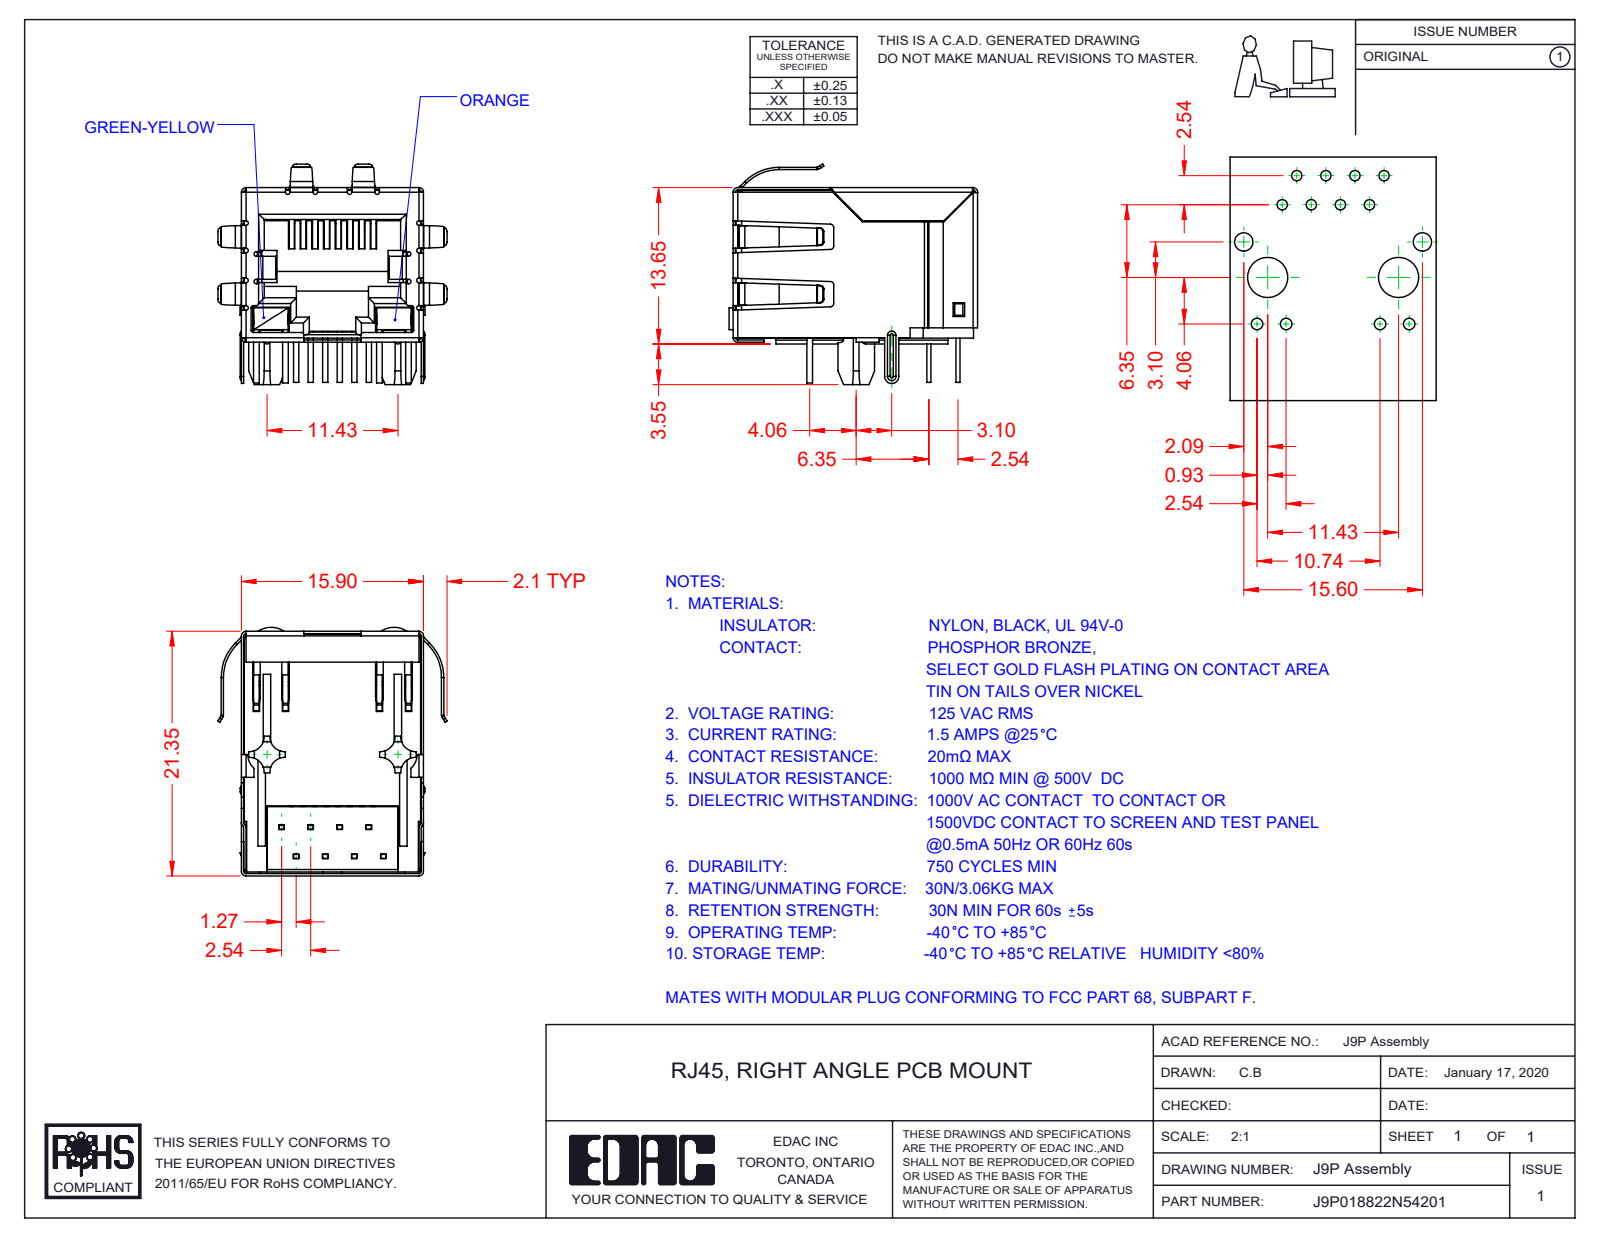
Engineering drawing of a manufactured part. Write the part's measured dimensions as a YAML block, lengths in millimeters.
part_name: "J9P018822N54202; 9P-LED LED RH_4-Orange; 9P-LED Contact Lock; 9P-LED LED LH_5-Green-Yellow (+4 more)"
step_written_by: "SolidWorks 2016 (CONFIG_CONTROL_DESIGN)"
units: millimeters
bodies: {solids: 13, faces: 1474, planar: 1042, cylindrical: 338, other: 94}
overall_size: [21.7, 20, 19.25]
volume: 2687
surface_area: 7515
partial_cylinders:
  - {radius: 0.2, count: 39}
  - {radius: 0.5, count: 22}
  - {radius: 0.3, count: 20}
  - {radius: 0.4, count: 16}
  - {radius: 1.3, count: 8}
  - {radius: 0.23, count: 5}
  - {radius: 0.11, count: 4}
  - {radius: 0.31, count: 4}
face_to_face_distances: [15.45, 15.7, 15.65, 0.35, 0.54, 15.5, 12.36, 0.6, 1.4, 0.59]
